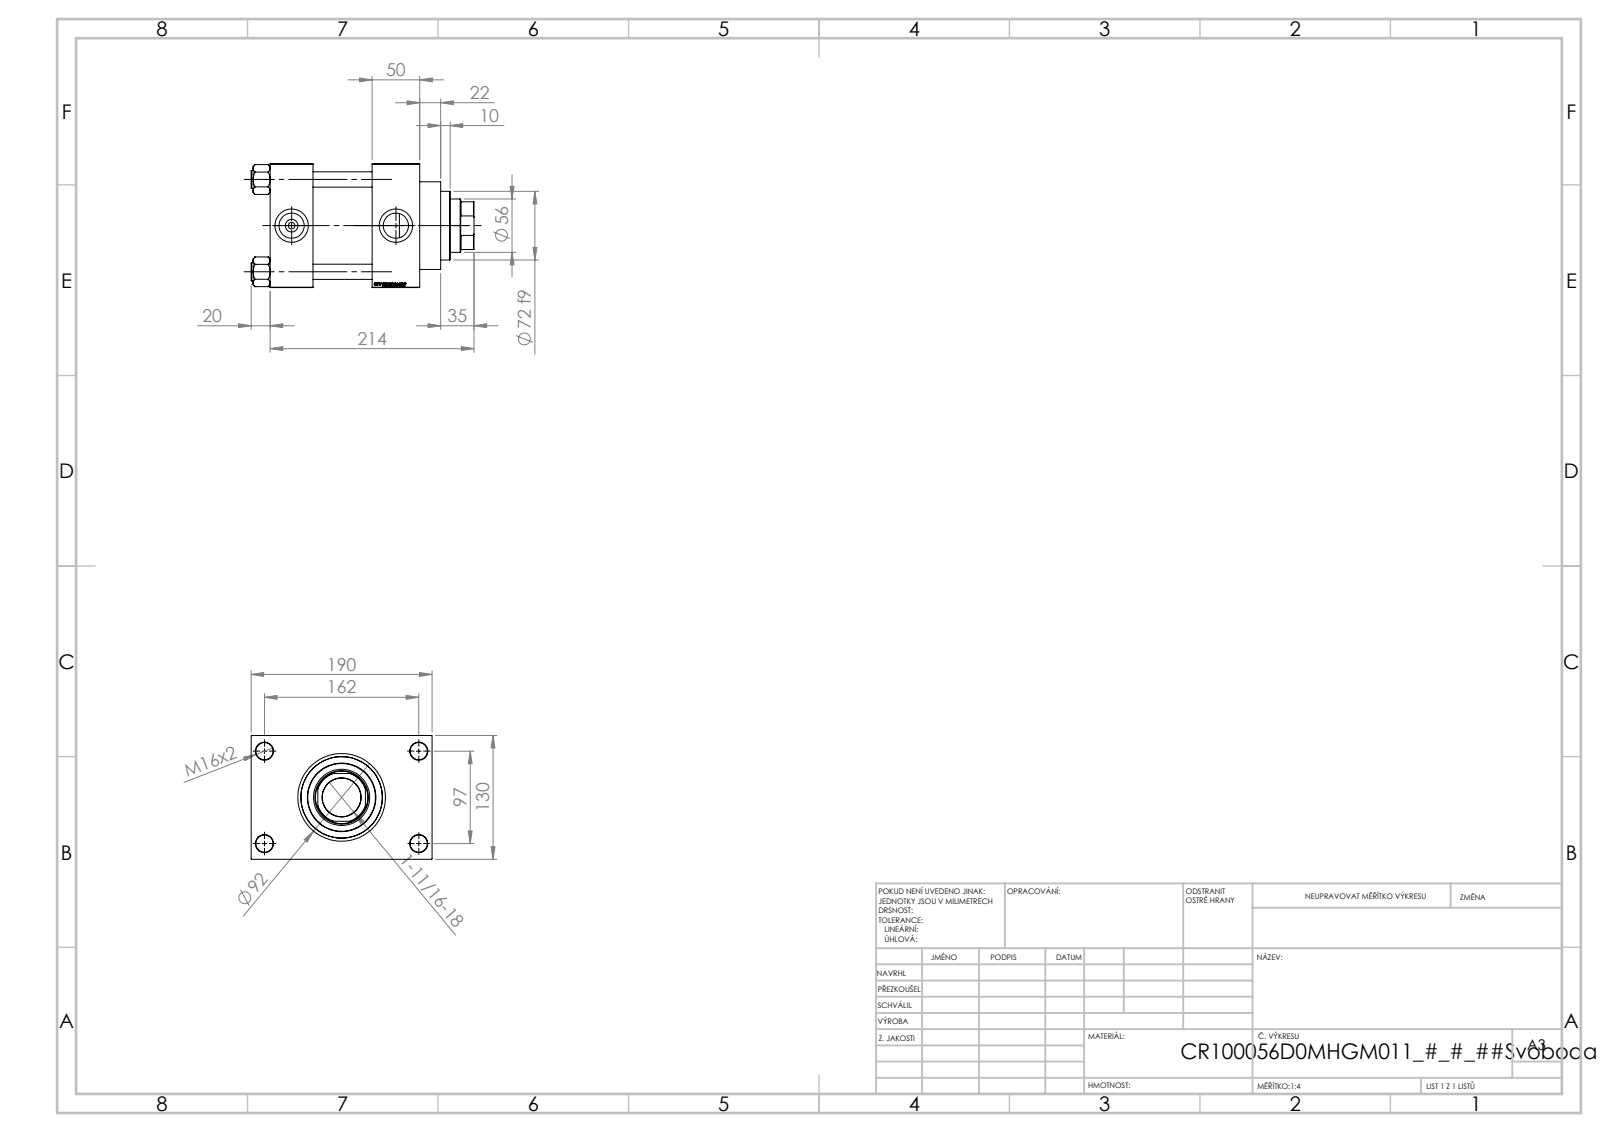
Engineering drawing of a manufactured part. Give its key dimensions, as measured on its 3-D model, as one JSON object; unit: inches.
{"part_name": "V215CR_D_TYCINKA; V215CR_VCP_D; V215_VC_A; NUT_M5_D (+1 more)", "step_written_by": "SolidWorks 2019 (CONFIG_CONTROL_DESIGN)", "units": "inches", "bodies": {"solids": 11, "faces": 1151, "planar": 545, "cylindrical": 88, "other": 518}, "overall_size": [9.213, 7.48, 5.118], "volume_in3": 158.1, "surface_area_in2": 547.4, "round_holes": [[0.63, 4], [0.709, 4], [0.276, 2], [1.041, 2], [1.378, 2], [1.594, 1], [2.205, 1], [2.323, 1], [2.992, 1], [3.366, 1], [3.937, 1]], "round_bosses_or_shafts": [[0.748, 4], [4.173, 1], [3.622, 1], [2.835, 1]], "partial_cylinders_radius": [[1.063, 1]], "face_to_face_distances": [5.118, 4.213, 1.969, 1.772, 2.441, 6.181, 4.409, 1.181, 6.299, 0.433], "hole_center_spacings": [1.281, 2.698, 3.717, 3.815, 4.026, 5.096, 6.367, 3.819]}
